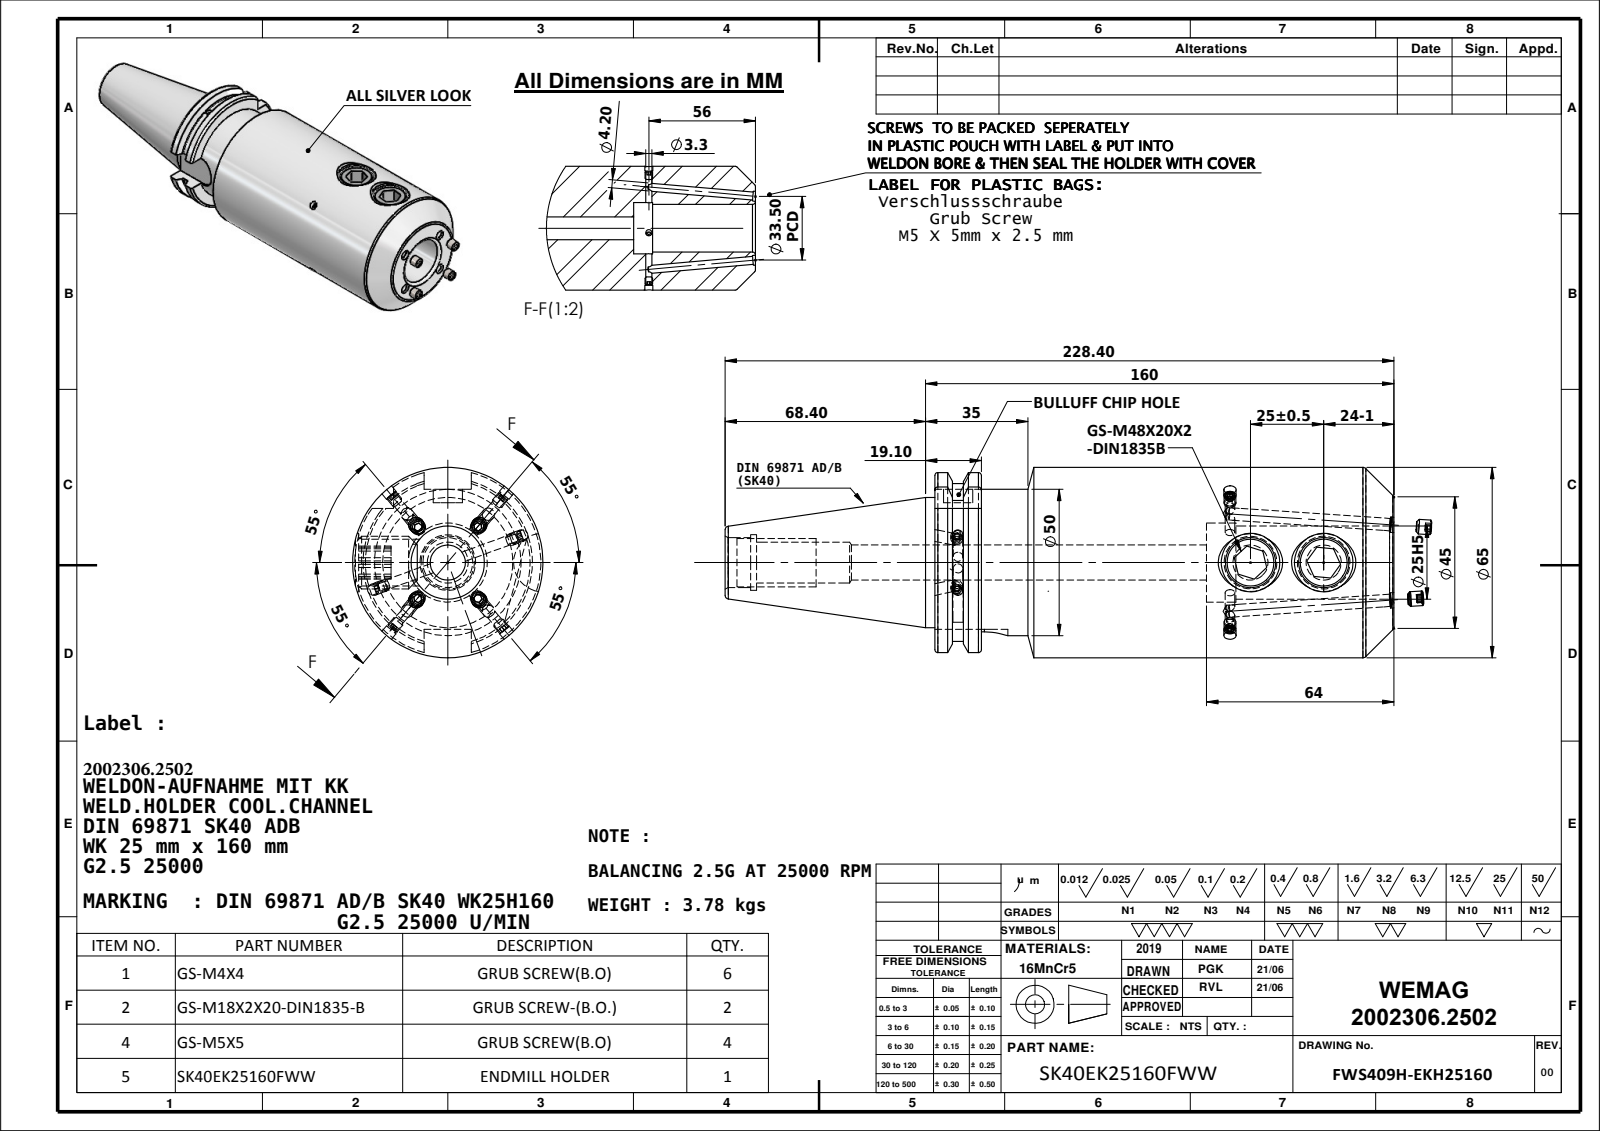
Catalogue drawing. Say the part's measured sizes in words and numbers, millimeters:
The part is named "91406-WK225160". Its 3-D file was written by "SolidWorks 2018 (CONFIG_CONTROL_DESIGN)". It is 1 solid with 189 faces: 41 planar, 88 cylindrical and 60 other. Overall it measures 228.4 by 65 by 65 millimeters. Its volume is 478 016 cubic millimeters and its surface area 63 537 square millimeters. Round holes: 7 of diameter 4.2, 4 of diameter 3.3, 4 of diameter 5.2, 2 of diameter 16, 2 of diameter 20, 1 of diameter 10, 1 of diameter 12, 1 of diameter 14, 1 of diameter 17, 1 of diameter 19, 1 of diameter 25, 1 of diameter 27. Round bosses or shafts: 1 of diameter 65, 1 of diameter 50, 1 of diameter 44.45. Partial cylindrical surfaces (rounded edges, fillets, slot ends): 1 of radius 8.05, 1 of radius 28.12, 1 of radius 31.77. The main face-to-face distances are 15.9, 156.8, 140.9, 92.8, 76.9, 64, 16.1, 47.8, 22.35, 38.45. The hole center spacings are 25.
